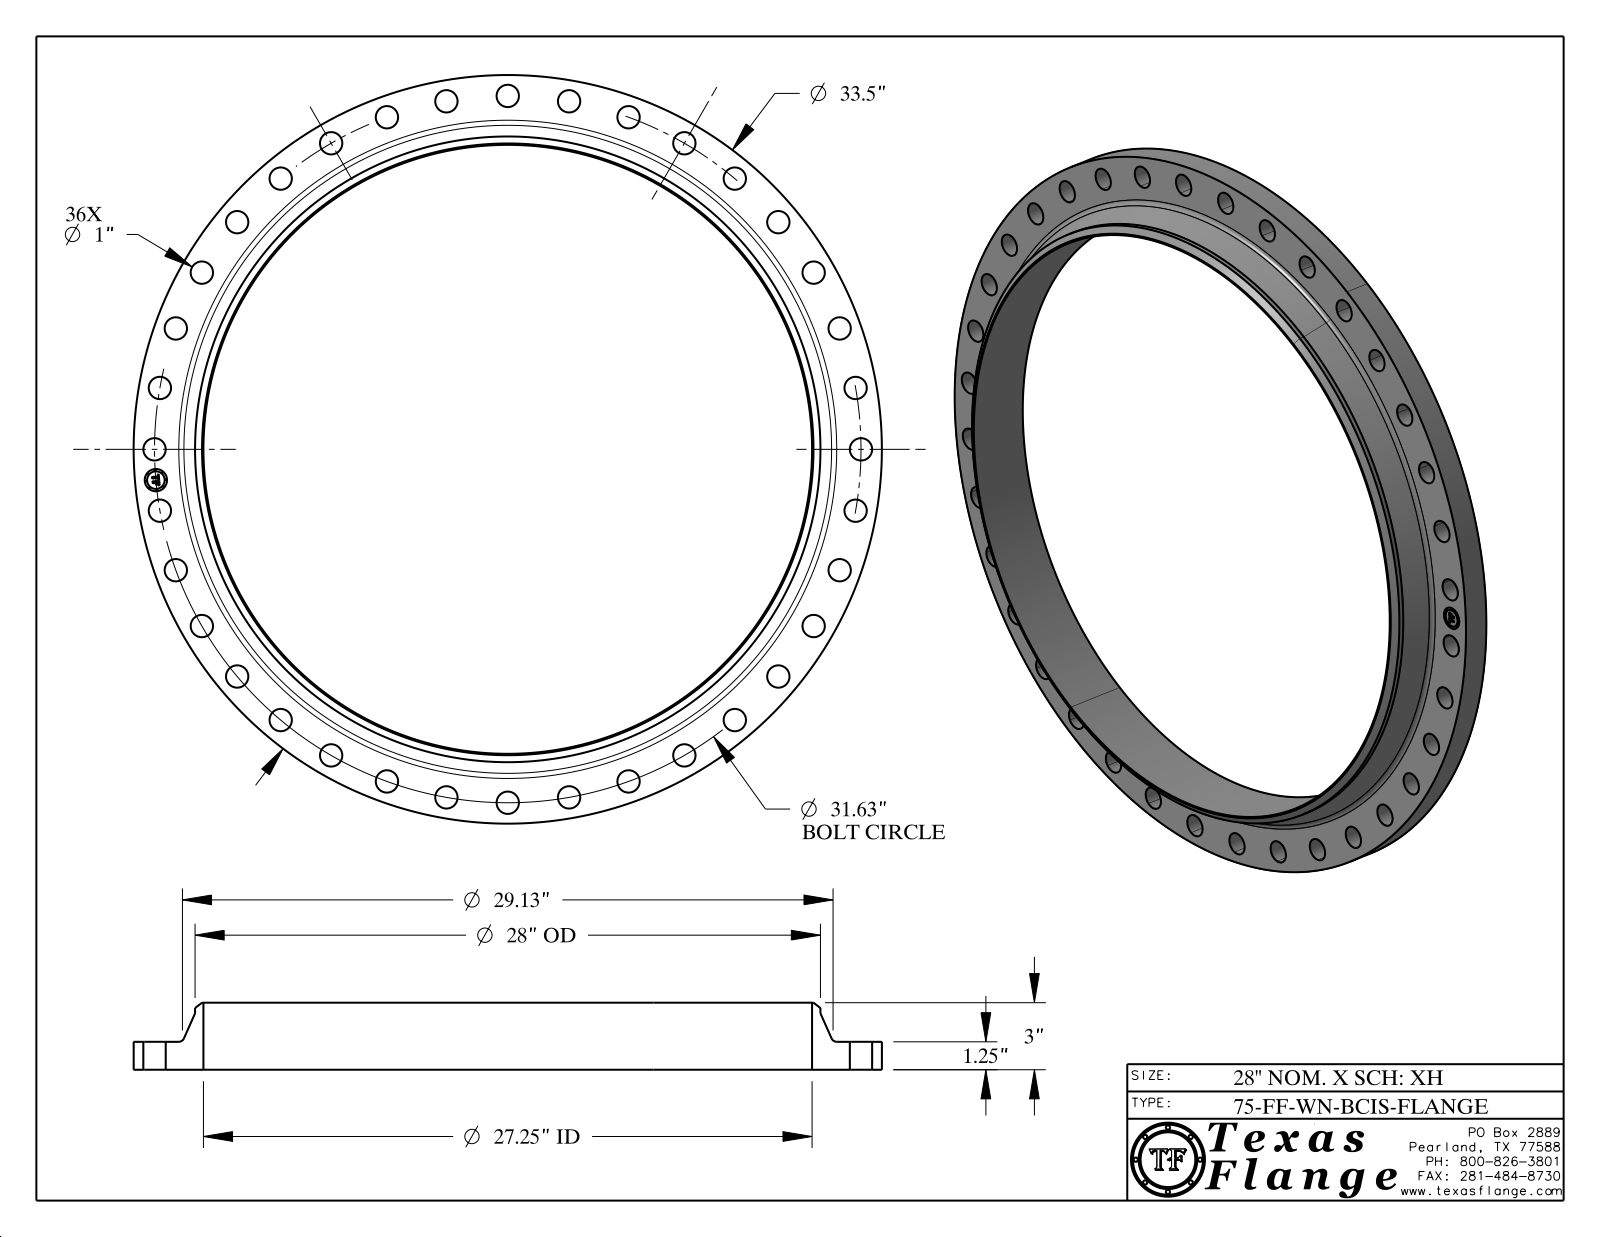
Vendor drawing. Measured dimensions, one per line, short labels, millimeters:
name: 75-FF-WN, BCIS
written by: CATIA V5 STEP AP214 (AUTOMOTIVE_DESIGN)
unit: mm
bodies: 1 solid, 472 faces (368 planar, 98 cylindrical, 6 other)
size: 850.9 × 850.9 × 76.2
volume: 6 942 000 mm³; area: 754 200 mm²
holes: 37× ⌀25.4, 1× ⌀692.2
bosses: 8× ⌀1.5, 1× ⌀850.9, 1× ⌀711.2, 1× ⌀20
face distances: 31.8, 76.2, 44.5, 0.4, 31.4, 44.8, 7.6, 7.4, 1.4, 4.9
hole spacings: 401.7, 139.5, 274.8, 70, 339.5, 728.1, 754.9, 800.4
